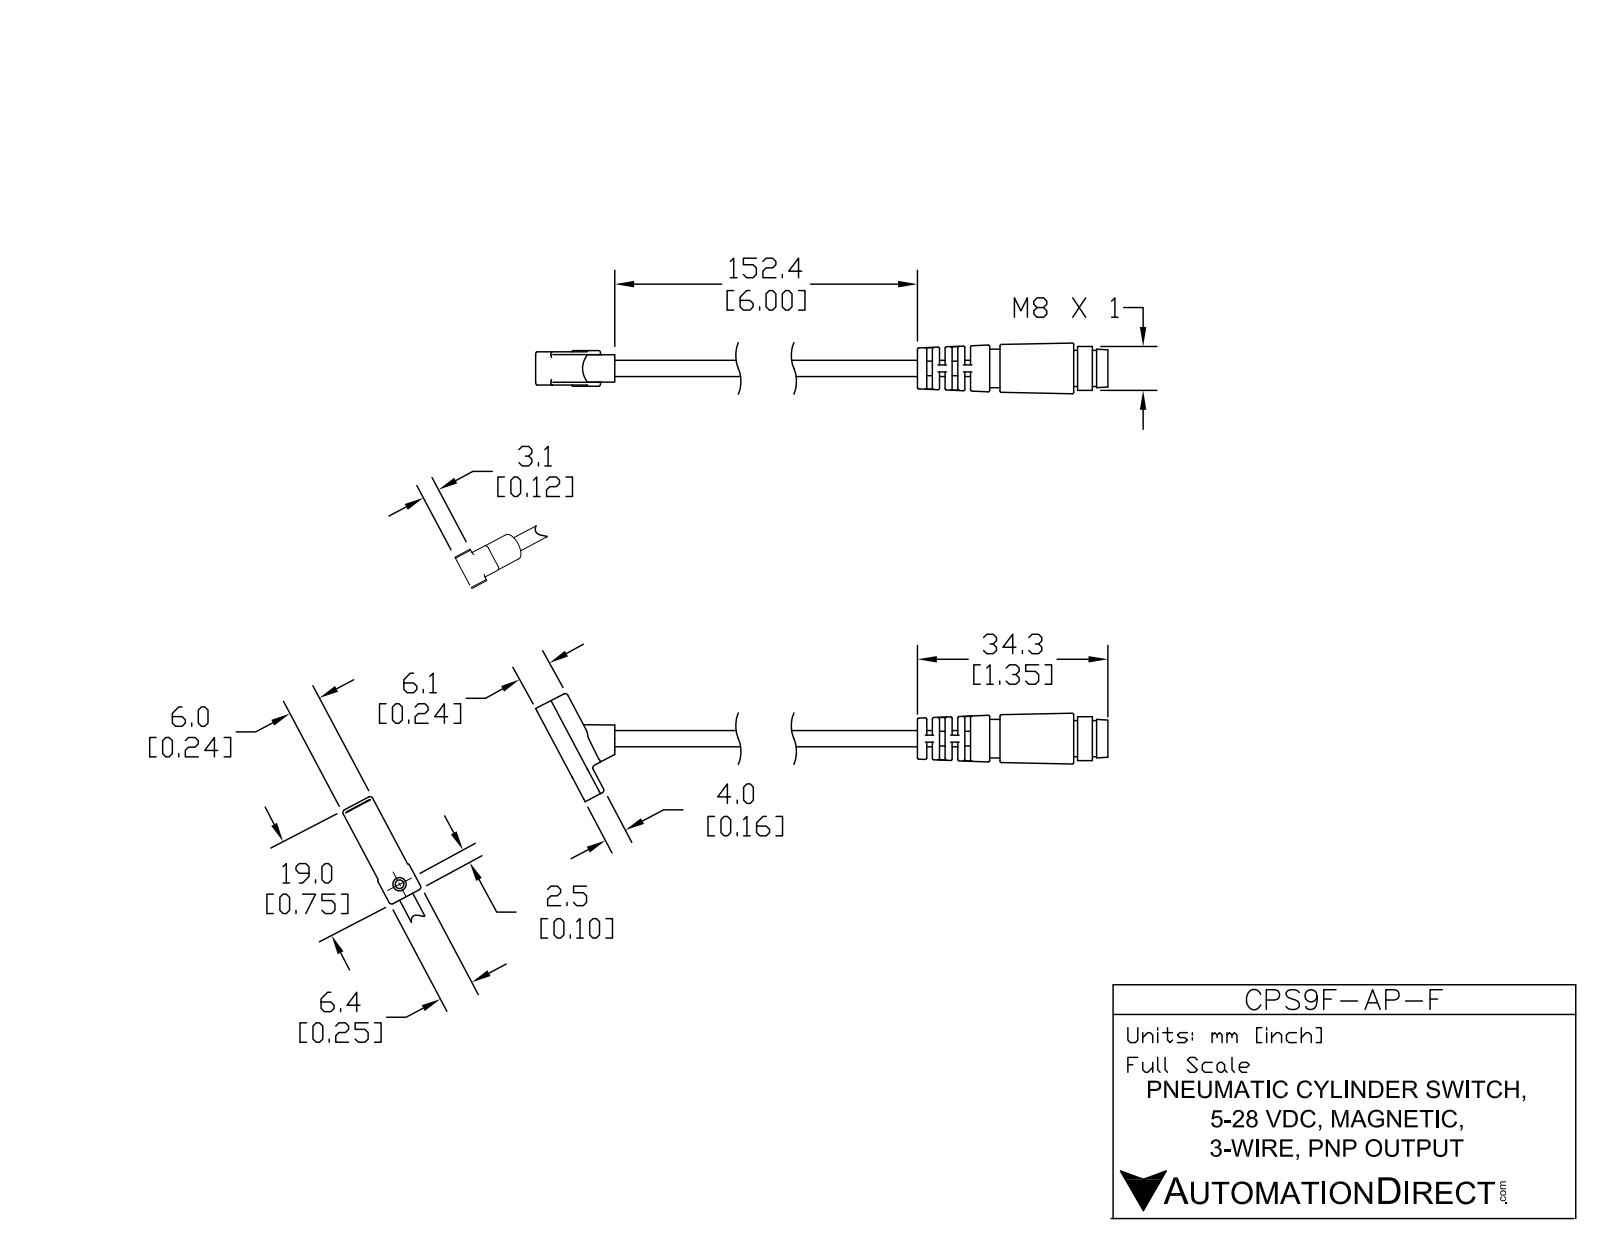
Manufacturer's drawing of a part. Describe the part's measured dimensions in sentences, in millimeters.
The part is named "CPS9F-AP-F". Its 3-D file was written by "SolidWorks 2014 (AUTOMOTIVE_DESIGN)". It is 5 solids with 260 faces: 85 planar, 96 cylindrical and 79 other. Overall it measures 143.4 by 84.5 by 9.1 millimeters. Its volume is 2 980 cubic millimeters and its surface area 3 091 square millimeters. Round holes: 1 of diameter 2.4, 1 of diameter 5.8. Round bosses or shafts: 3 of diameter 1, 1 of diameter 7.9, 1 of diameter 6.9, 1 of diameter 6.5, 1 of diameter 2.9, 1 of diameter 2.9. Partial cylindrical surfaces (rounded edges, fillets, slot ends): 23 of radius 0.1, 18 of radius 0.5, 2 of radius 0.2, 2 of radius 0.6, 1 of radius 2.5. The main face-to-face distances are 1.3, 2.3, 4.6, 0.5, 1, 2.3, 3.3, 5, 5.5, 1.
